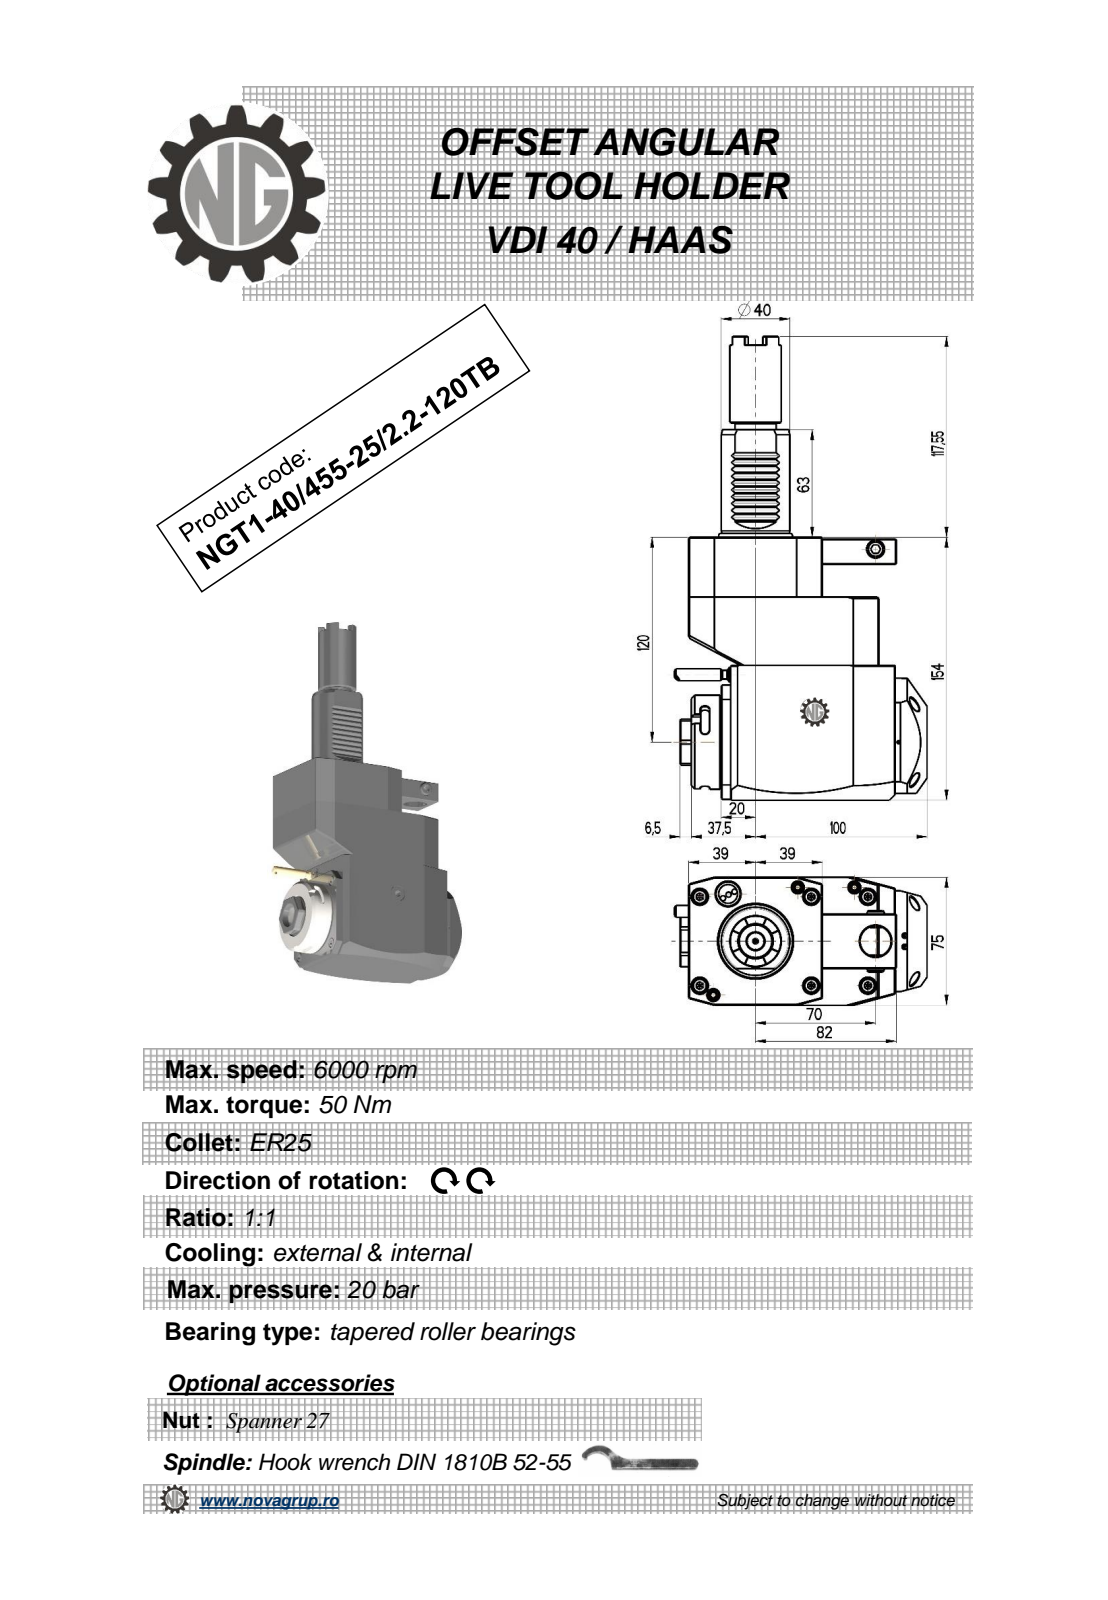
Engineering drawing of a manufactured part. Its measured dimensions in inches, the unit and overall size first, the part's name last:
Units: inches
Overall size (bounding box): 10.691 × 5.8 × 2.953
Round holes (diameter × count): ⌀0.709 ×2, ⌀0.098 ×1, ⌀0.118 ×1, ⌀0.374 ×1, ⌀0.787 ×1
Round bosses / shafts (diameter × count): ⌀0.353 ×2, ⌀2.165 ×1, ⌀1.89 ×1, ⌀1.575 ×1, ⌀1.181 ×1, ⌀0.945 ×1, ⌀0.394 ×1, ⌀0.276 ×1
Partial cylindrical surfaces — rounded edges, fillets, slot ends (radius × count): R0.012 ×10, R0.098 ×6, R7.087 ×2, R0.02 ×1, R0.167 ×1, R0.591 ×1, R0.965 ×1, R1.476 ×1
Main face-to-face distances: 2.953, 6.063, 0.748, 4.685, 2.323, 4.37, 3.622, 1.378, 0.689, 2.106
Hole centre spacings: 1.701, 2.756, 2.956, 4.429
Volume: 79.88 in³ · Surface area: 147.7 in²
Bodies: 1 solid, 376 faces (216 planar, 76 cylindrical, 84 other)
Part name (STEP PRODUCT): NGT1_40_455_25_1_2_120TB
STEP written by: PRO/ENGINEER BY PARAMETRIC TECHNOLOGY CORPORATION, 2010280 (CONFIG_CONTROL_DESIGN)
